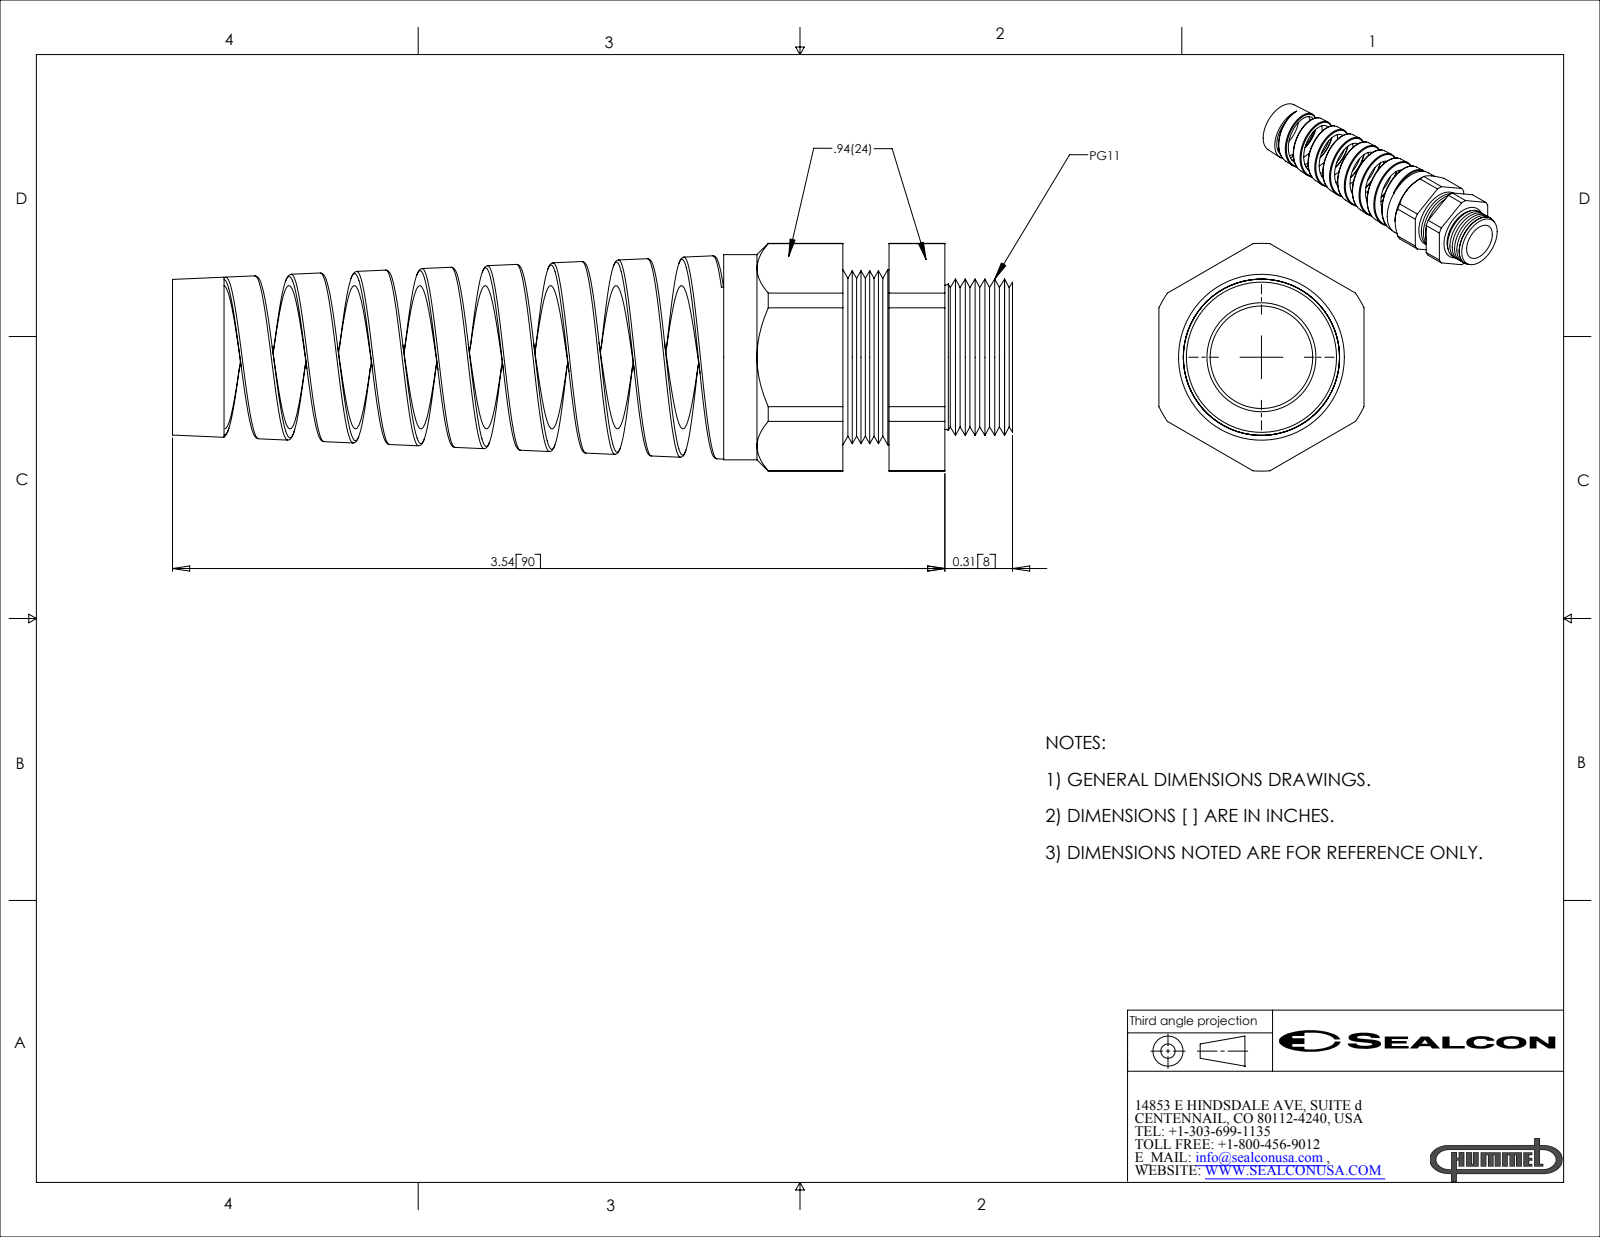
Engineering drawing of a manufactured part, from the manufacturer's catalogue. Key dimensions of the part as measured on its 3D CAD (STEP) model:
Part name (STEP PRODUCT): CF11GA-GY
STEP written by: SolidWorks 2007 (CONFIG_CONTROL_DESIGN)
Units: inches
Bodies: 2 solids, 152 faces (24 planar, 41 cylindrical, 87 other)
Overall size (bounding box): 3.85 × 1.043 × 0.94
Volume: 0.81 in³ · Surface area: 20.21 in²
Round holes (diameter × count): ⌀0.47 ×1, ⌀0.657 ×1
Round bosses / shafts (diameter × count): ⌀0.94 ×1, ⌀0.803 ×1
Partial cylindrical surfaces — rounded edges, fillets, slot ends (radius × count): R0.339 ×1, R0.522 ×1
Main face-to-face distances: 0.94, 0.468, 0.212, 0.256, 0.778, 0.566, 0.31, 0.546, 0.758, 1.014
